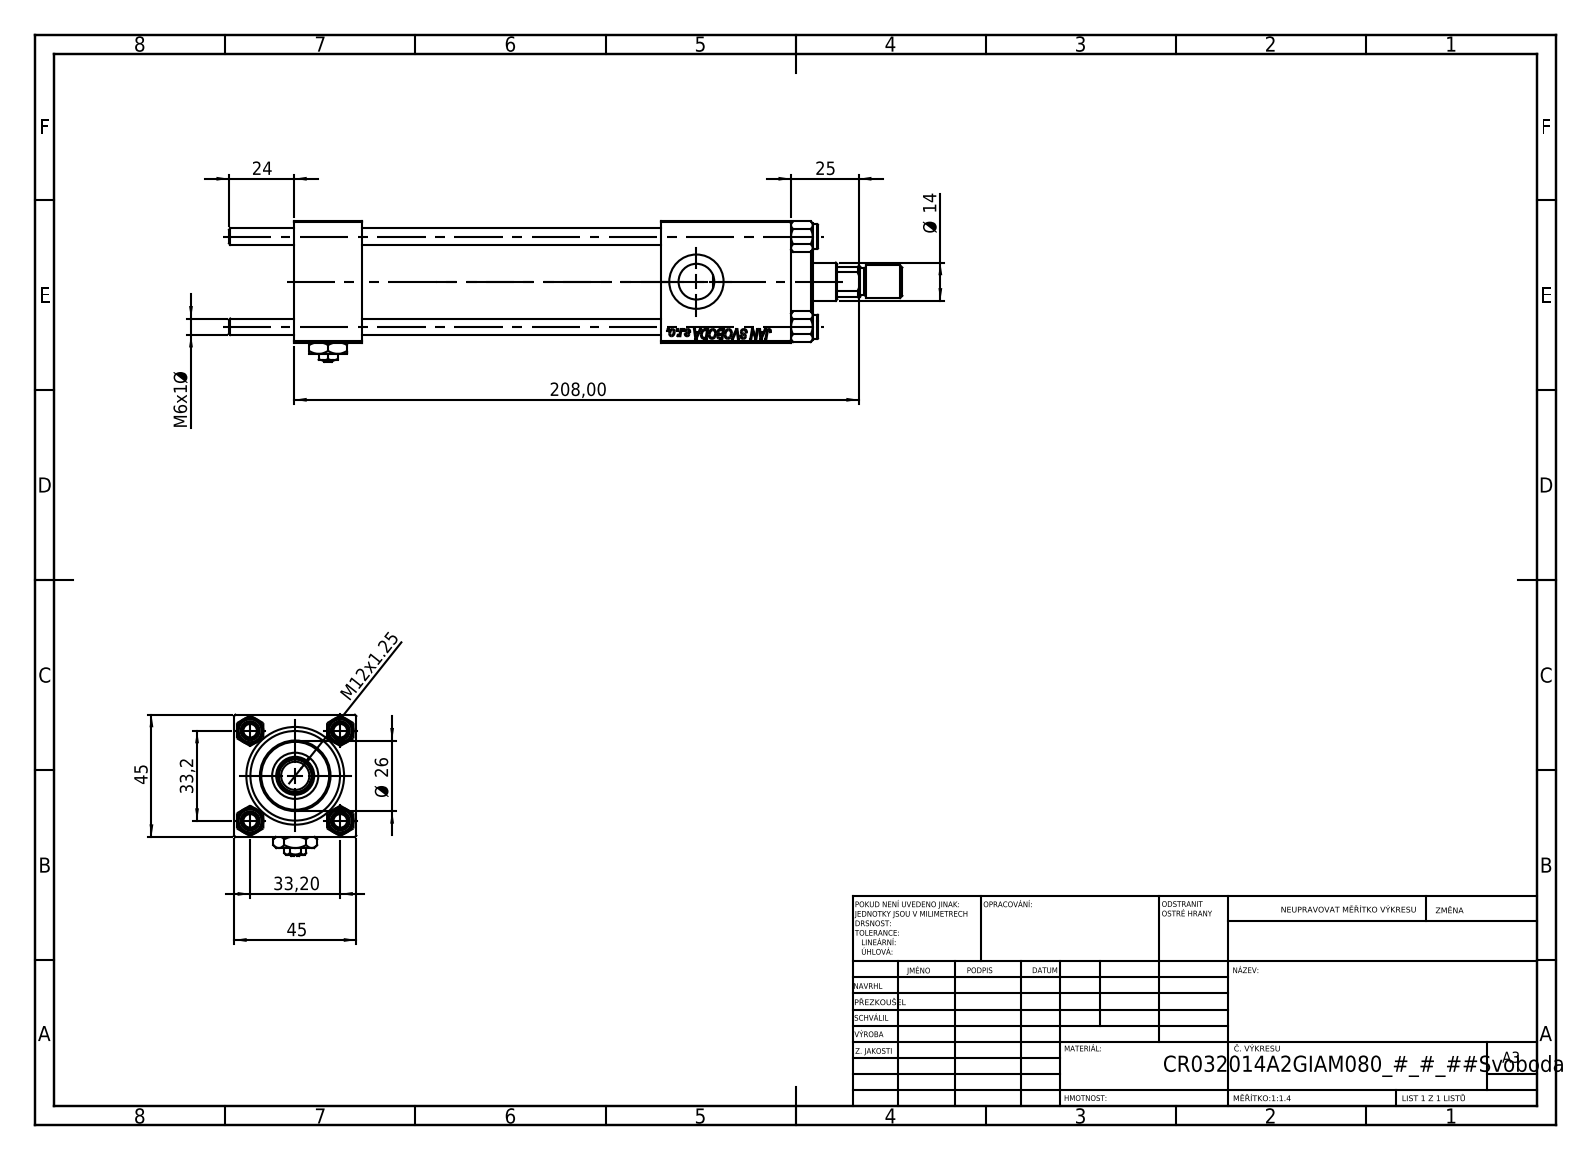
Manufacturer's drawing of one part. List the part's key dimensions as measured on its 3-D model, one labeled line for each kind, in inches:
Part name (STEP PRODUCT): CR025_012_A_0_G_A_G_M_020_+#_##_TYCINKA; V215CR_VCP; Zatka_pro_OIL_PORT; ROD_END_AH (+3 more)
STEP written by: SolidWorks 2019 (CONFIG_CONTROL_DESIGN)
Units: inches
Bodies: 13 solids, 1198 faces (546 planar, 88 cylindrical, 564 other)
Overall size (bounding box): 9.764 × 2.047 × 1.772
Volume: 14.34 in³ · Surface area: 147.4 in²
Round holes (diameter × count): ⌀0.236 ×4, ⌀0.276 ×2, ⌀0.518 ×2, ⌀0.787 ×2, ⌀0.256 ×1, ⌀0.551 ×1, ⌀0.669 ×1, ⌀0.945 ×1, ⌀1.26 ×1, ⌀1.299 ×1
Round bosses / shafts (diameter × count): ⌀0.354 ×4, ⌀1.496 ×1, ⌀1.024 ×1, ⌀0.472 ×1, ⌀0.394 ×1
Partial cylindrical surfaces — rounded edges, fillets, slot ends (radius × count): R0.256 ×1
Main face-to-face distances: 1.772, 0.984, 7.205, 6.22, 5.315, 4.331, 1.89, 6.075, 5.091, 0.76
Hole centre spacings: 0.924, 1.307, 1.848
